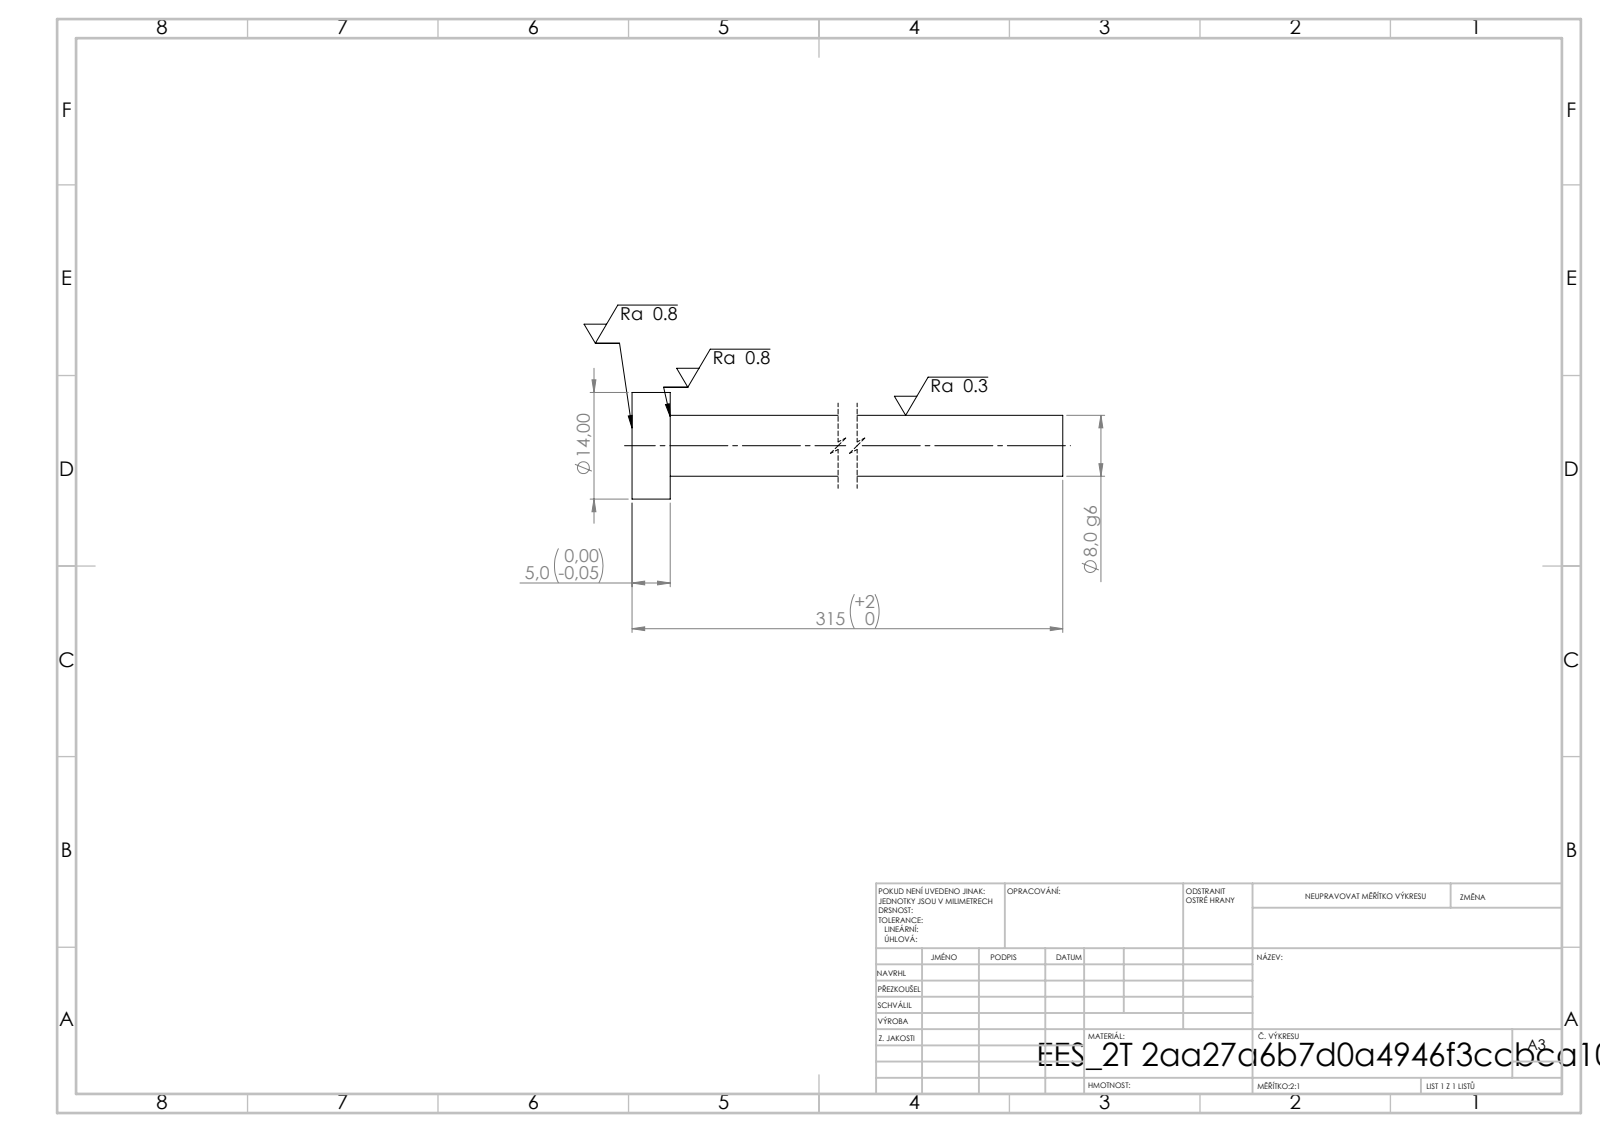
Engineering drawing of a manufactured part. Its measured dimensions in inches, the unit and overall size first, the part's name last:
Units: inches
Overall size (bounding box): 12.402 × 0.551 × 0.551
Round bosses / shafts (diameter × count): ⌀0.551 ×1, ⌀0.315 ×1
Main face-to-face distances: 0.197, 12.402, 12.205
Volume: 0.998 in³ · Surface area: 12.89 in²
Bodies: 1 solid, 7 faces (3 planar, 4 cylindrical, 0 other)
STEP written by: SolidWorks 2019 (CONFIG_CONTROL_DESIGN)
